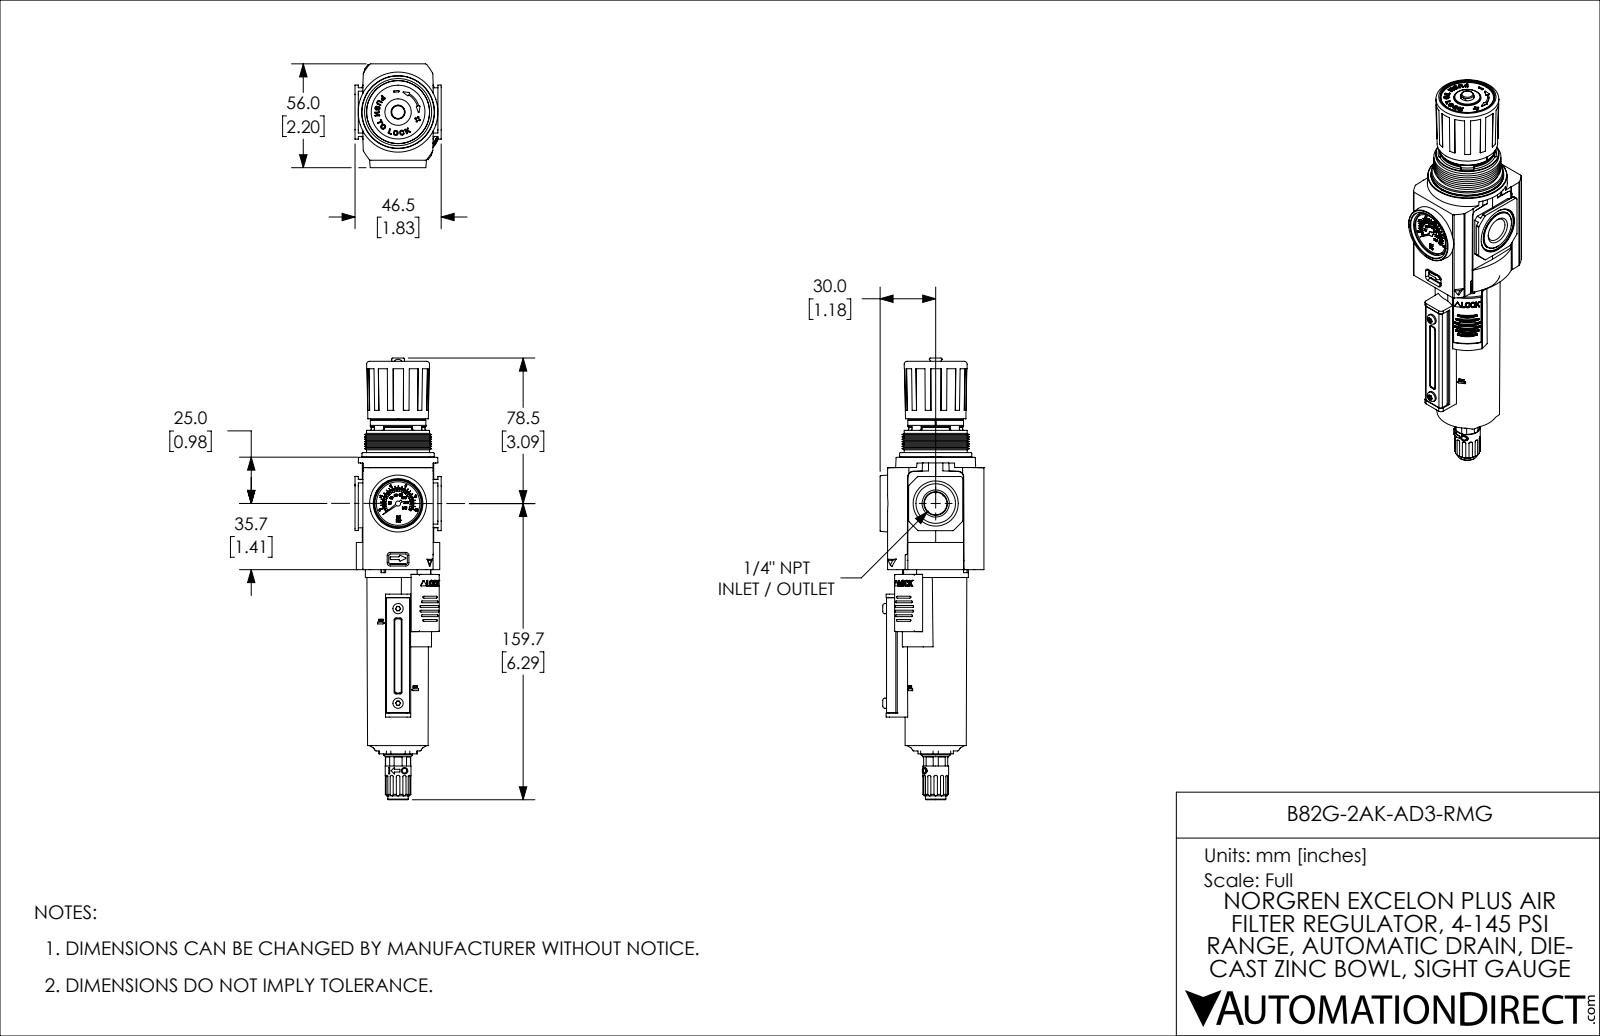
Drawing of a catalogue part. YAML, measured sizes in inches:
part_name: "B82G-2AK-AD3-RMG"
step_written_by: "SolidWorks 2021 (CONFIG_CONTROL_DESIGN)"
units: inches
bodies: {solids: 8, faces: 2693, planar: 1022, cylindrical: 1268, other: 403}
overall_size: [9.379, 2.205, 1.831]
volume: 16.9
surface_area: 114.4
round_holes:
  - {diameter: 0.097, count: 4}
  - {diameter: 0.138, count: 2}
  - {diameter: 0.098, count: 1}
  - {diameter: 0.128, count: 1}
  - {diameter: 0.197, count: 1}
  - {diameter: 0.236, count: 1}
  - {diameter: 0.259, count: 1}
  - {diameter: 0.628, count: 1}
  - {diameter: 0.925, count: 1}
  - {diameter: 1.102, count: 1}
  - {diameter: 1.354, count: 1}
round_bosses_or_shafts:
  - {diameter: 0.224, count: 2}
  - {diameter: 0.217, count: 2}
  - {diameter: 0.118, count: 2}
  - {diameter: 1.535, count: 1}
  - {diameter: 1.388, count: 1}
  - {diameter: 1.356, count: 1}
  - {diameter: 1.339, count: 1}
  - {diameter: 1.291, count: 1}
partial_cylinders:
  - {radius: 0.02, count: 50}
  - {radius: 0.039, count: 50}
  - {radius: 0.009, count: 25}
  - {radius: 0.031, count: 20}
  - {radius: 0.006, count: 19}
  - {radius: 0.011, count: 13}
  - {radius: 0.012, count: 12}
  - {radius: 0.012, count: 12}
face_to_face_distances: [0.059, 1.988, 1.693, 0.354, 1.634, 0.295, 1.417, 1.475, 0.182, 1.352]
hole_center_spacings: [0.63, 1.091, 1.26, 2.705, 3.325, 2.965, 5.374, 5.402]
